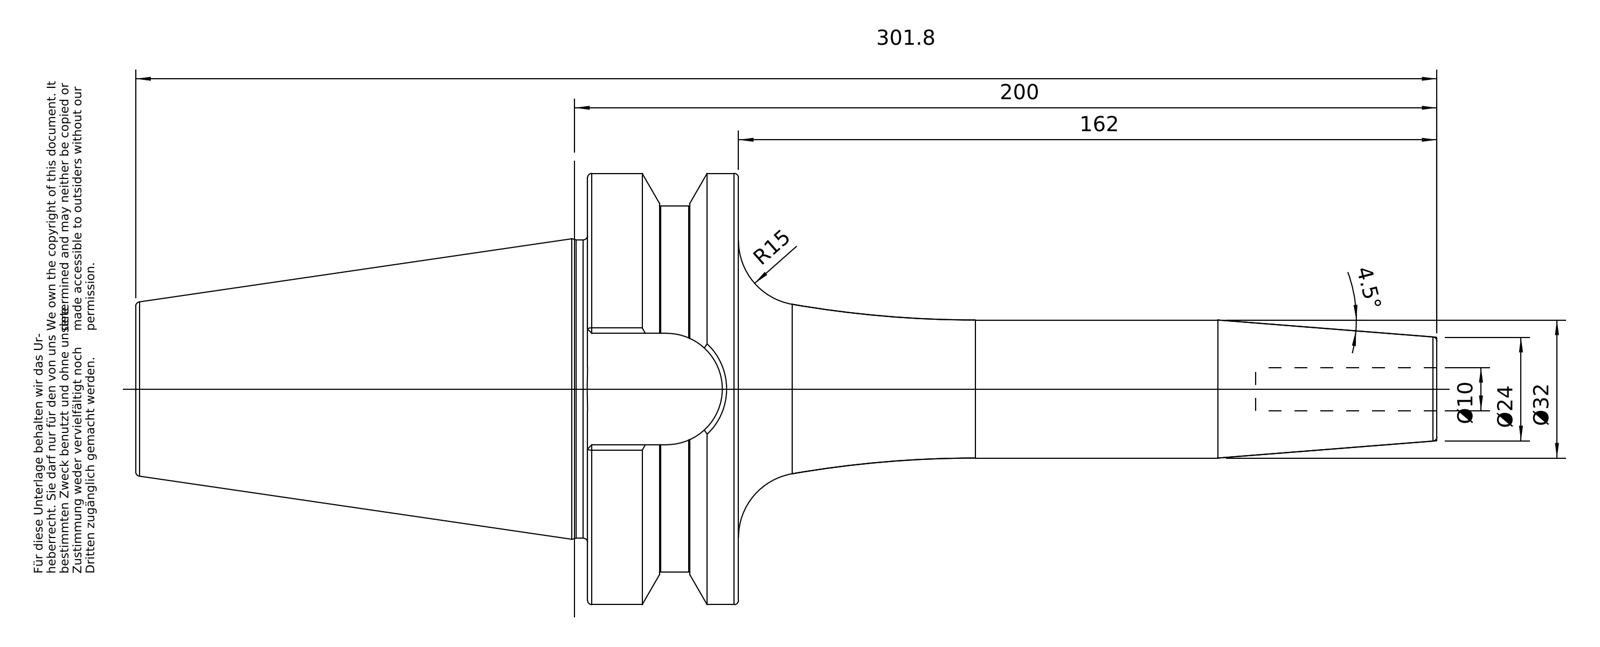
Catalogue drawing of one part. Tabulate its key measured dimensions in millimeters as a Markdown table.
| quantity | value |
| --- | --- |
| part name | 50-646-10 |
| STEP written by | PRO/ENGINEER BY PARAMETRIC TECHNOLOGY CORPORATION, 2010430 (CONFIG_CONTROL_DESIGN) |
| units | millimeters |
| bodies | 1 solid, 98 faces (26 planar, 22 cylindrical, 50 other) |
| overall size | 301.8 × 99.97 × 99.97 |
| volume | 602 836 mm³ |
| surface area | 67 995 mm² |
| round holes (diameter × count) | 10 × 1, 20.75 × 1, 25.02 × 1, 25.7 × 1 |
| round bosses / shafts (diameter × count) | 99.97 × 1, 84.75 × 1, 69.15 × 1, 32 × 1, 24.01 × 1 |
| partial cylindrical surfaces (radius × count) | 12.9 × 1 |
| main face-to-face distances | 35, 70.4, 104.8, 139.8, 25.8, 301.8, 197, 162, 48, 56.8 |
